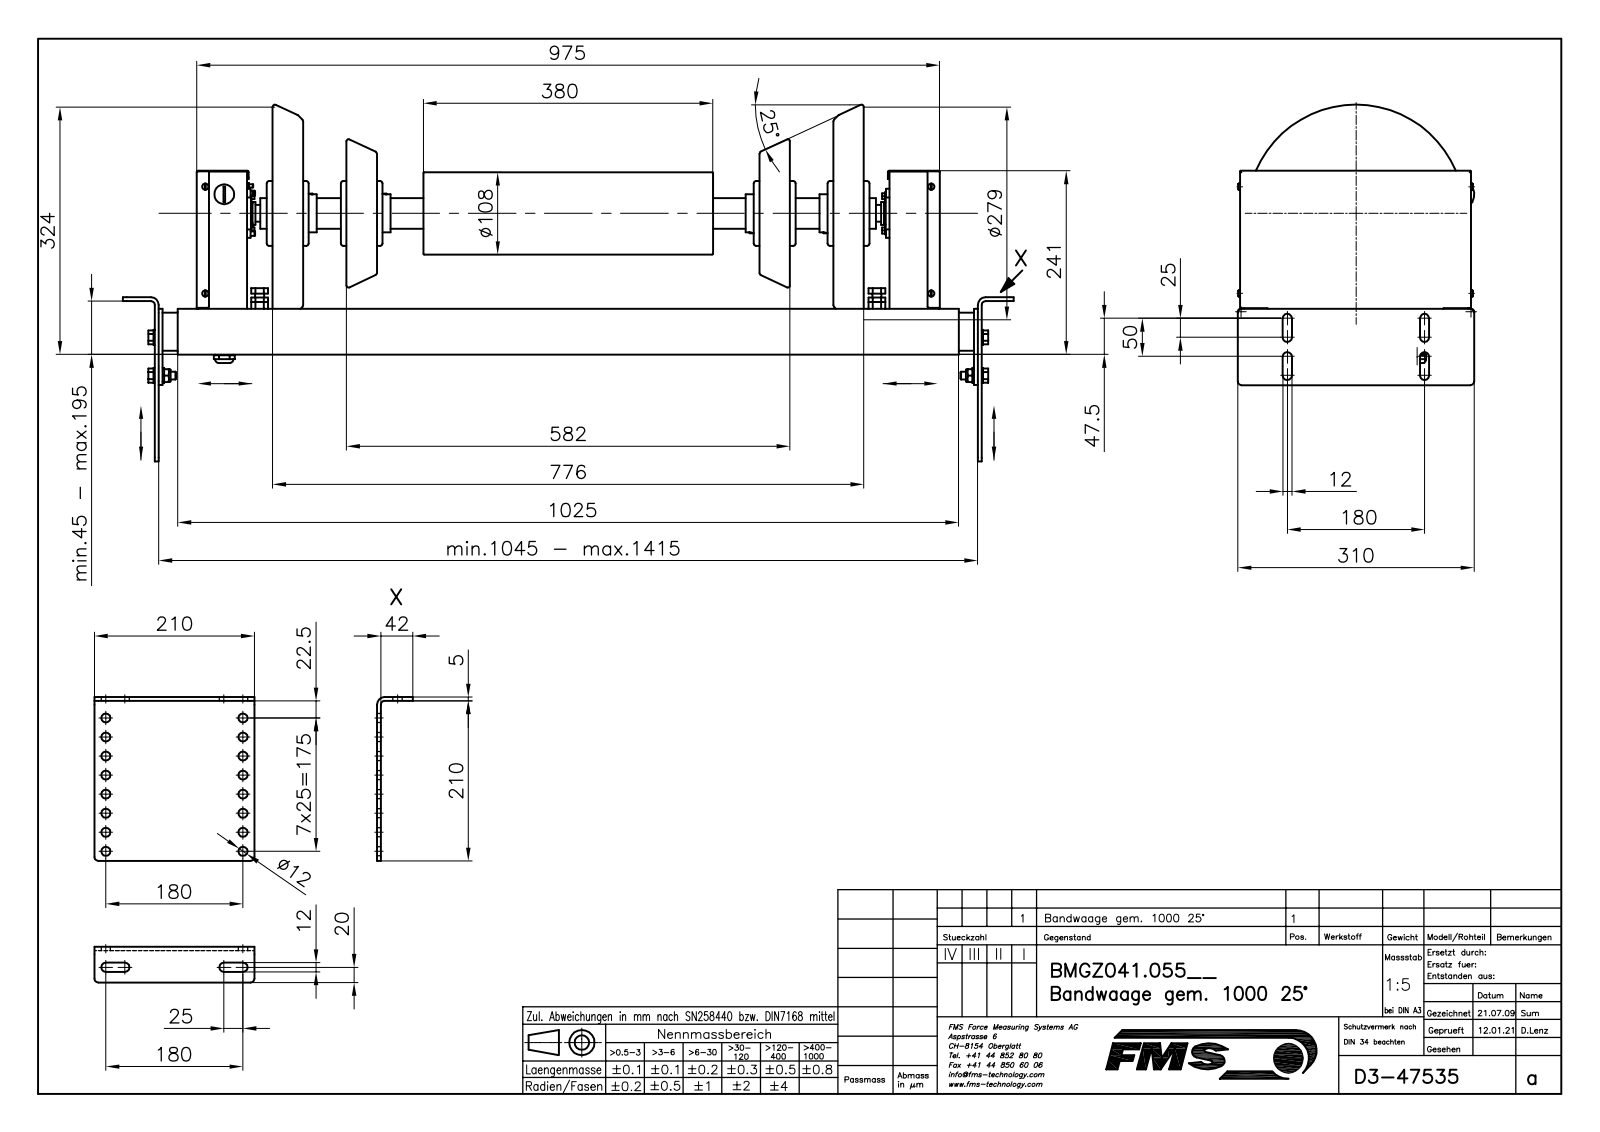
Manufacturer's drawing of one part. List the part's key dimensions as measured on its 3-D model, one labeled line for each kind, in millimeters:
Part name (STEP PRODUCT): B47535_STP; B50108; 6KT-SCHRAUBE_M12X30; ZYL_SCHR__M4X8 (+8 more)
STEP written by: Mechanical Desktop 2009 (CONFIG_CONTROL_DESIGN)
Units: millimetres
Bodies: 177 solids, 2962 faces (1429 planar, 1050 cylindrical, 483 other)
Overall size (bounding box): 1169 × 467.5 × 310.2
Volume: 8 398 000 mm³ · Surface area: 3 748 000 mm²
Round holes (diameter × count): ⌀12 ×17, ⌀5 ×6, ⌀3.5 ×4, ⌀4.9 ×4, ⌀6.4 ×4, ⌀6.91 ×4, ⌀8.68 ×4, ⌀8.75 ×4, ⌀10 ×4, ⌀10.5 ×4, ⌀10.68 ×4, ⌀14.8 ×4
Round bosses / shafts (diameter × count): ⌀12 ×11, ⌀8.2 ×8, ⌀4.2 ×8, ⌀20 ×6, ⌀10 ×6, ⌀8 ×6, ⌀5 ×5, ⌀16 ×4
Partial cylindrical surfaces — rounded edges, fillets, slot ends (radius × count): R2 ×34, R1 ×24, R4 ×16, R5 ×16, R6 ×12, R3.5 ×8, R2.25 ×6, R0.5 ×4
Main face-to-face distances: 4, 5, 1, 51, 270, 36, 56, 3, 50, 266
Hole centre spacings: 25, 181.73, 50, 186.82, 75, 195, 100, 180
